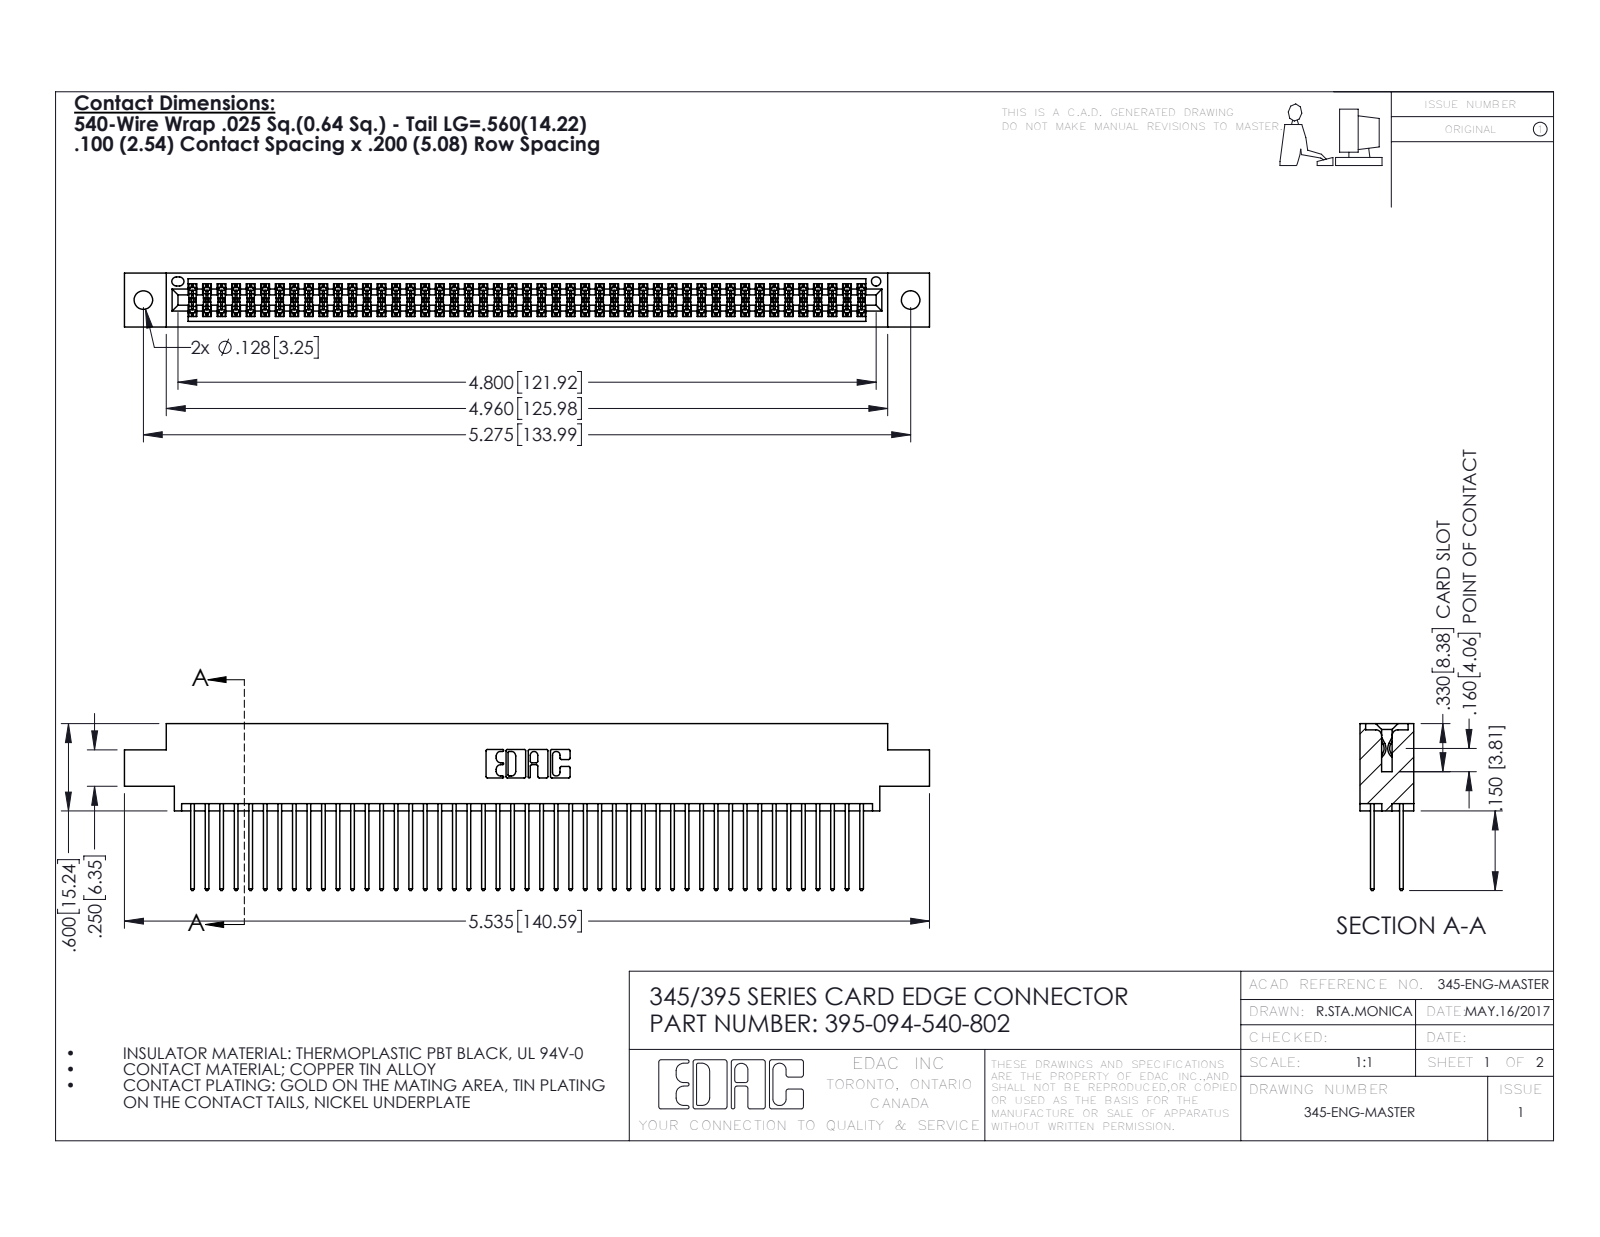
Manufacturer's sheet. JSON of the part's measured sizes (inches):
{"part_name": "345 Part_0.170 Offset - 0.128 Dia; 345-292-001_345-293-140; 395-094-540-802", "step_written_by": "SolidWorks 2016 (CONFIG_CONTROL_DESIGN)", "units": "inches", "bodies": {"solids": 95, "faces": 4830, "planar": 3186, "cylindrical": 1644, "other": 0}, "overall_size": [5.535, 1.147, 0.37], "volume_in3": 0.849, "surface_area_in2": 34.38, "round_holes": [[0.128, 2], [0.064, 1]], "partial_cylinders_radius": [[0.006, 141], [0.01, 94], [0.01, 22], [0.007, 6], [0.031, 6], [0.026, 3], [0.014, 2], [0.019, 2]], "face_to_face_distances": [0.298, 0.072, 0.2, 0.098, 0.272, 0.025, 0.37, 0.225, 0.175, 0.149], "hole_center_spacings": [0.27, 5.039, 5.275]}
